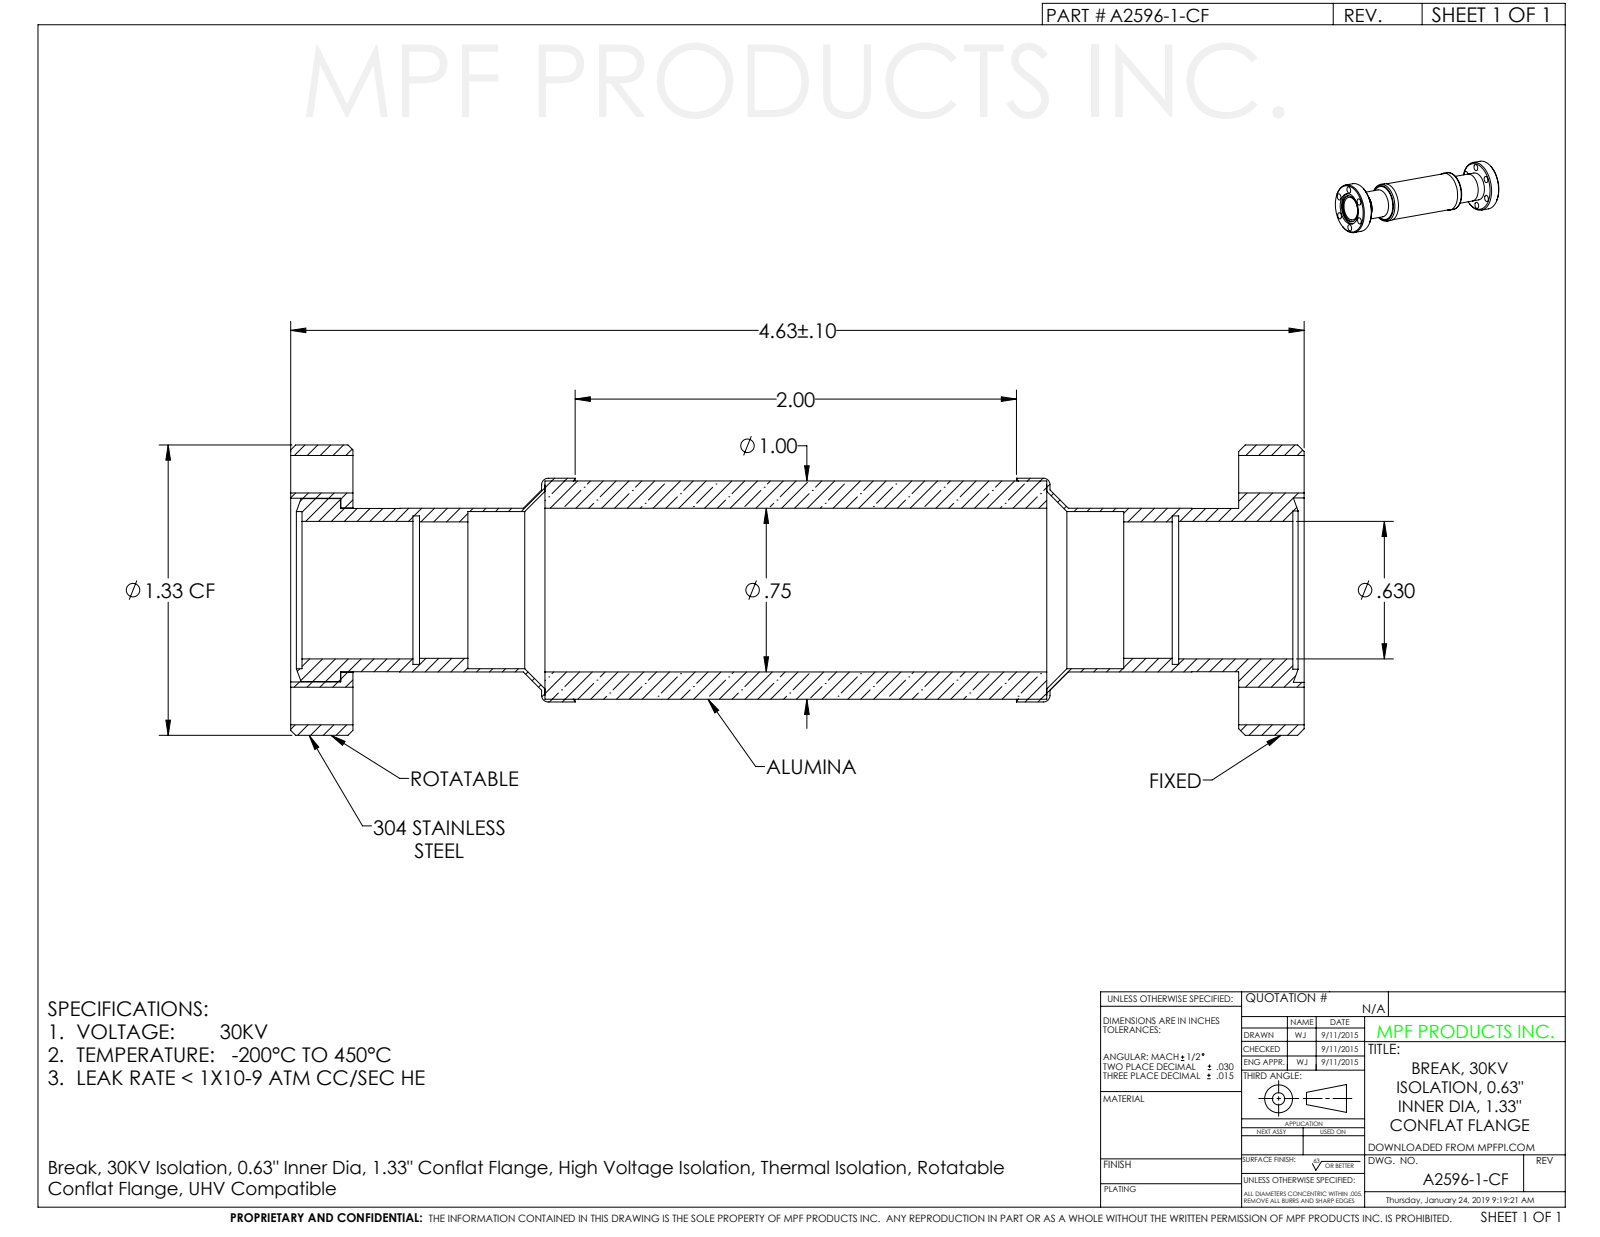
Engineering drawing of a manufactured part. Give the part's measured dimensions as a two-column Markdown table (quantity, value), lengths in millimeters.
| quantity | value |
| --- | --- |
| part name | A2596-1-CF |
| STEP written by | SolidWorks 2012 (CONFIG_CONTROL_DESIGN) |
| units | millimeters |
| bodies | 1 solid, 146 faces (26 planar, 84 cylindrical, 36 other) |
| overall size | 118 × 33.8 × 33.8 |
| volume | 24 070 mm³ |
| surface area | 22 040 mm² |
| round holes (diameter × count) | 4.4 × 12, 15.9 × 1, 16 × 1, 17.3 × 1, 18.3 × 1, 18.3 × 1, 18.4 × 1, 19.2 × 1, 21.5 × 1, 21.6 × 1, 25.5 × 1 |
| round bosses / shafts (diameter × count) | 33.8 × 1, 26.3 × 1, 26.2 × 1, 25.4 × 1, 21.3 × 1, 19.1 × 1, 19 × 1, 17 × 1 |
| main face-to-face distances | 103.6, 7.1, 110.7, 118, 110.8, 7.2, 29.6, 22.5, 81.1, 88.3 |
| hole center spacings | 13.5, 13.5, 23.1, 23.3, 23.6, 26.9, 0.4, 13.1 |
